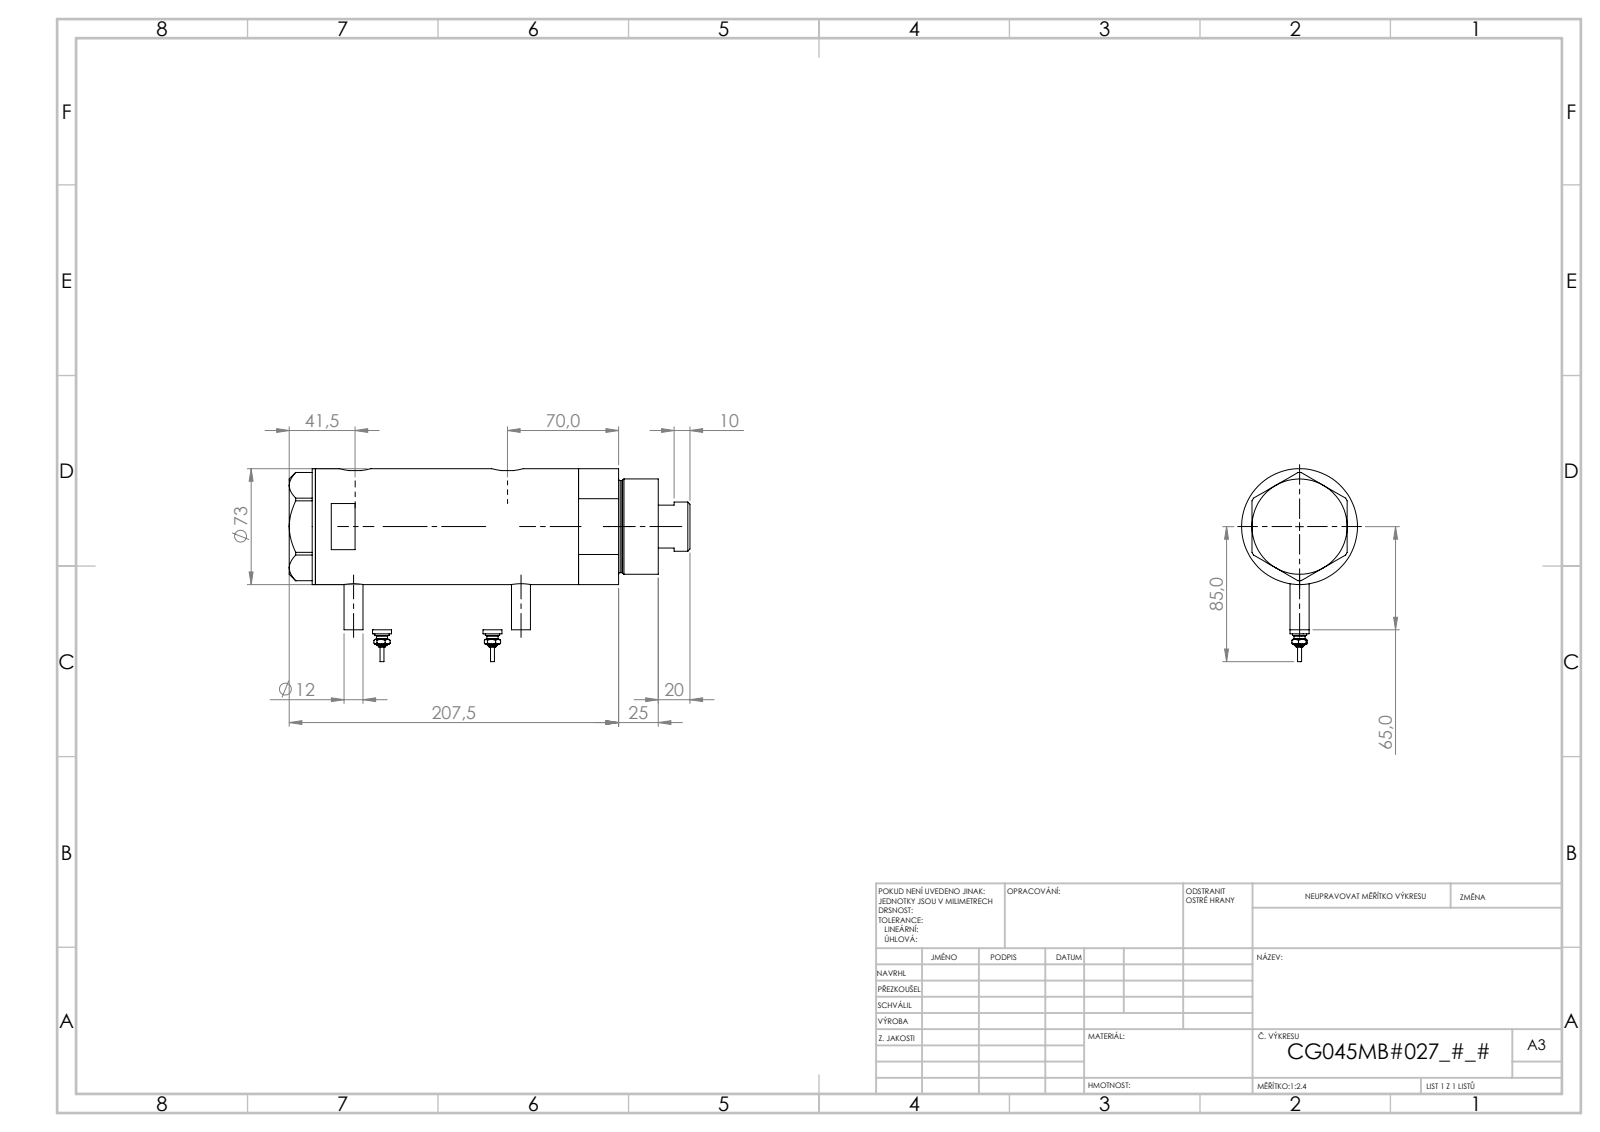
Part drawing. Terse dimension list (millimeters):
name: V270CG_FRONT; V270CG_MIDDLE; Switch; V270CG_VC (+1 more)
written by: SolidWorks 2019 (CONFIG_CONTROL_DESIGN)
unit: mm
bodies: 6 solids, 212 faces (77 planar, 71 cylindrical, 64 other)
size: 252.5 × 121.5 × 73
volume: 910 241 mm³; area: 152 669 mm²
holes: 2× ⌀12.5, 2× ⌀13.16, 1× ⌀10.5, 1× ⌀32, 1× ⌀33.5, 1× ⌀45, 1× ⌀48, 1× ⌀64
bosses: 4× ⌀12, 2× ⌀9, 2× ⌀7, 2× ⌀4.5, 2× ⌀2.5, 1× ⌀73, 1× ⌀60, 1× ⌀58
rounds: 2× R10
face distances: 95, 121, 26, 16.5, 42.5, 137.5, 2, 216, 232.5, 190
hole spacings: 1, 8.5, 96, 97, 104.5, 105.5
